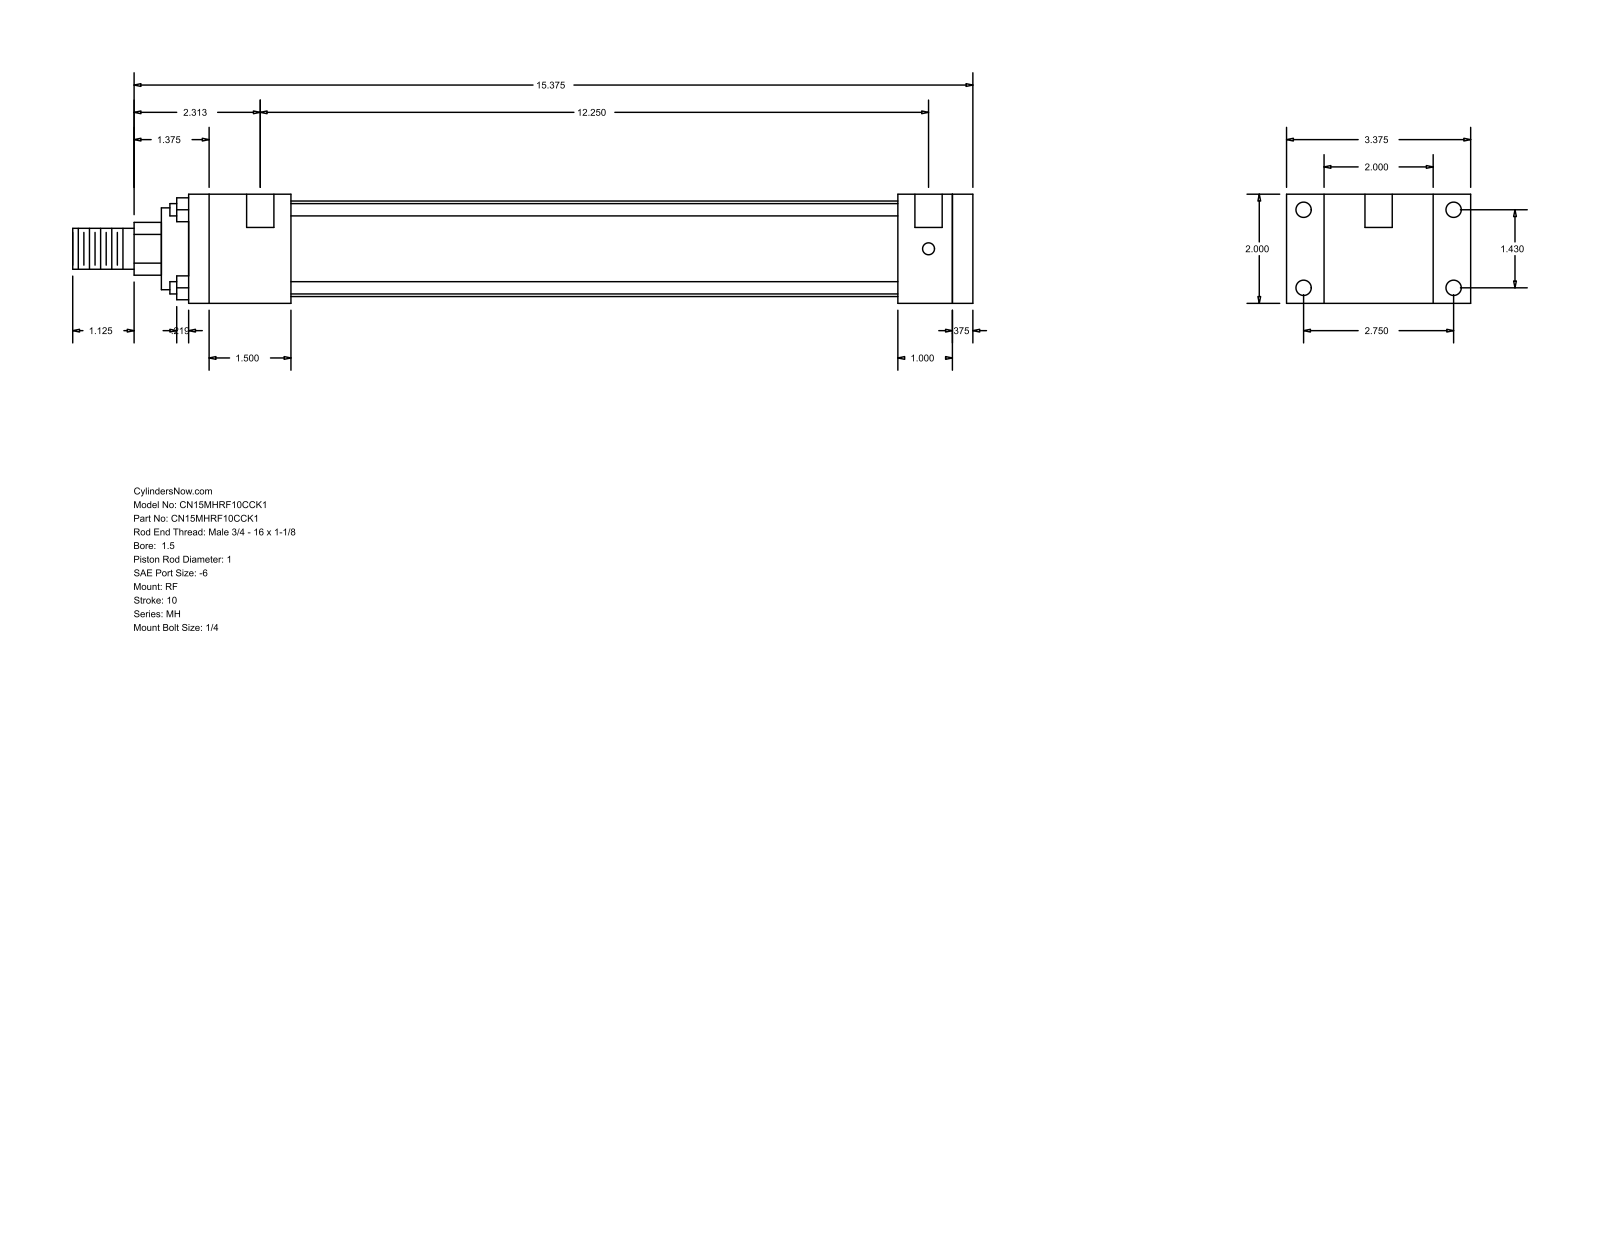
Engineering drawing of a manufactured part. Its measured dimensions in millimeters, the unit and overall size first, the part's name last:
Units: millimetres
Overall size (bounding box): 419.1 × 85.72 × 50.8
Round holes (diameter × count): ⌀5.56 ×4, ⌀7.14 ×4, ⌀12.7 ×2
Round bosses / shafts (diameter × count): ⌀5.71 ×4, ⌀44.45 ×1, ⌀38.1 ×1, ⌀25.4 ×1, ⌀19.05 ×1
Partial cylindrical surfaces — rounded edges, fillets, slot ends (radius × count): R12.29 ×1
Main face-to-face distances: 50.8, 9.52, 355.6, 25.4, 365.12, 17.46, 68.26, 330.2, 34.92, 47.63
Hole centre spacings: 36.32, 69.84, 78.72, 314.33, 3.18, 311.15
Bodies: 0 solids, 92 faces (64 planar, 28 cylindrical, 0 other)
Part name (STEP PRODUCT): MH_RF__0150_1
STEP written by: GSSL Pune (CONFIG_CONTROL_DESIGN)
